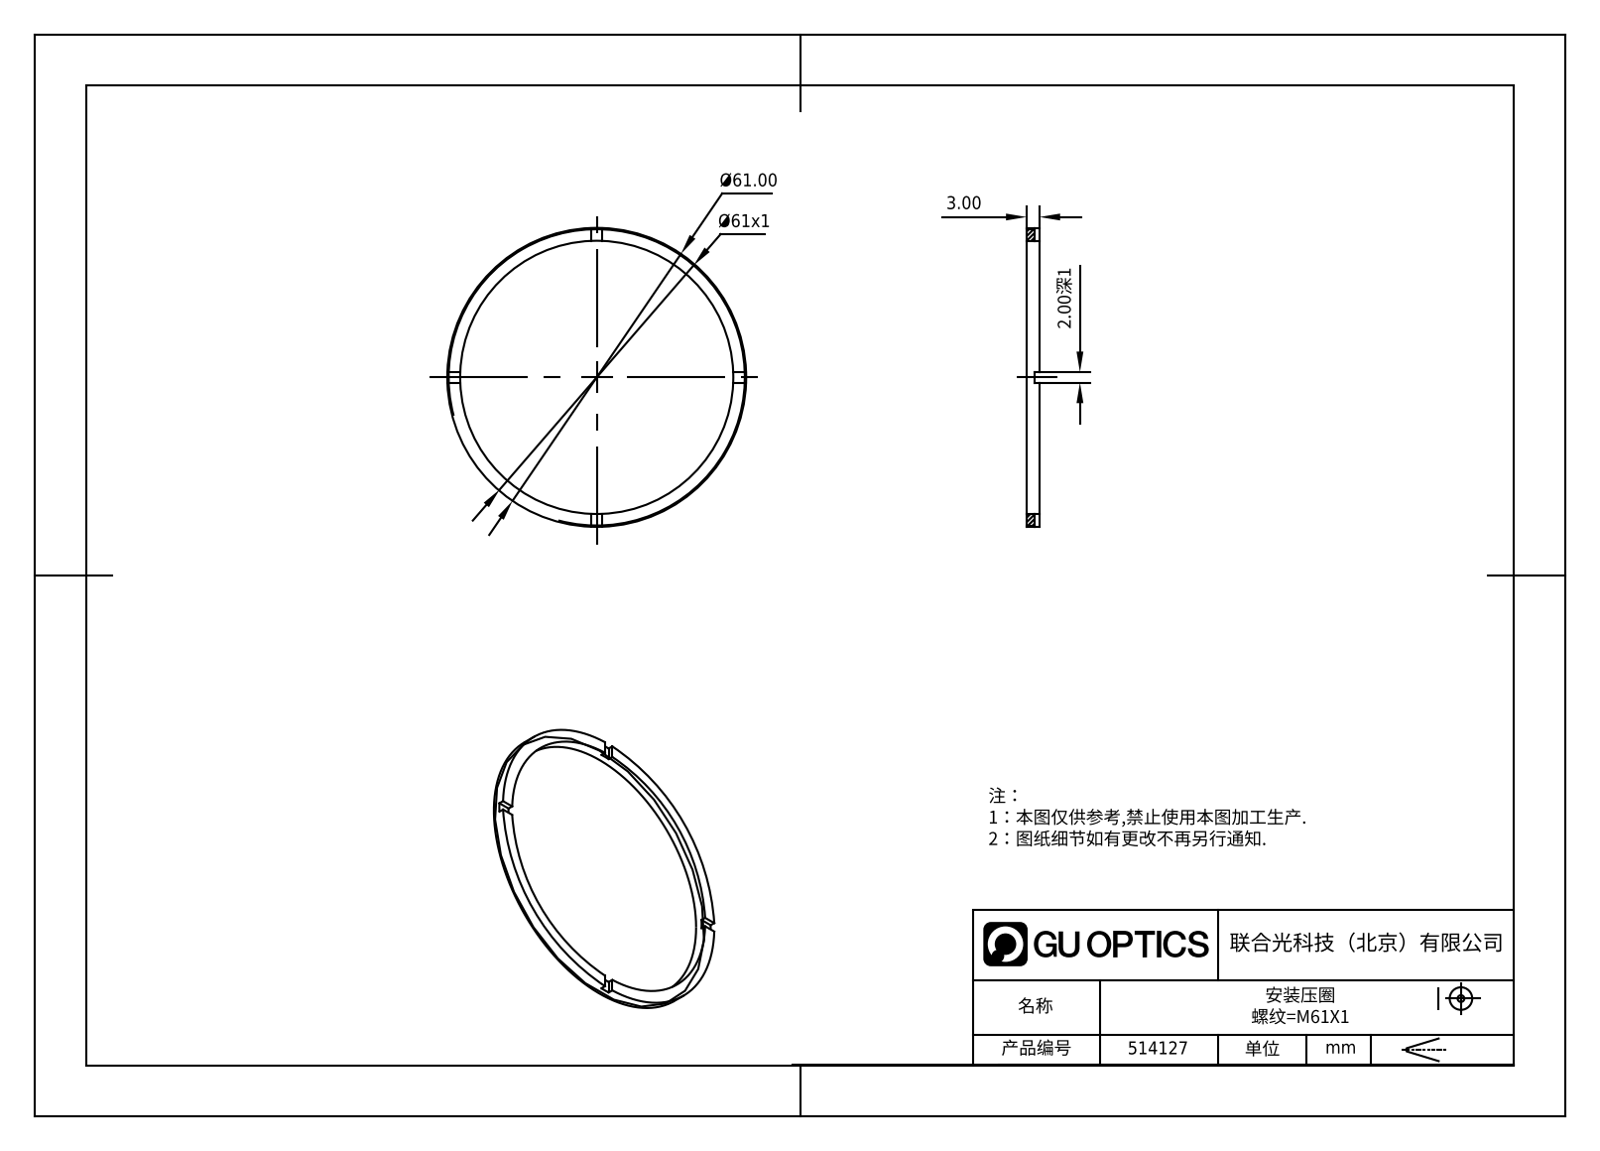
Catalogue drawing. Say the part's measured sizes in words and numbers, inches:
The part is named "514127". Its 3-D file was written by "SolidWorks 2020 (CONFIG_CONTROL_DESIGN)". It is 1 solid with 21 faces: 17 planar, 4 cylindrical and 0 other. Overall it measures 2.402 by 2.402 by 0.118 inches. Its volume is 0.083 cubic inches and its surface area 3.14 square inches. Round holes: 1 of diameter 2.205. Round bosses or shafts: 1 of diameter 2.402. The main face-to-face distances are 0.118, 0.079, 0.039.
